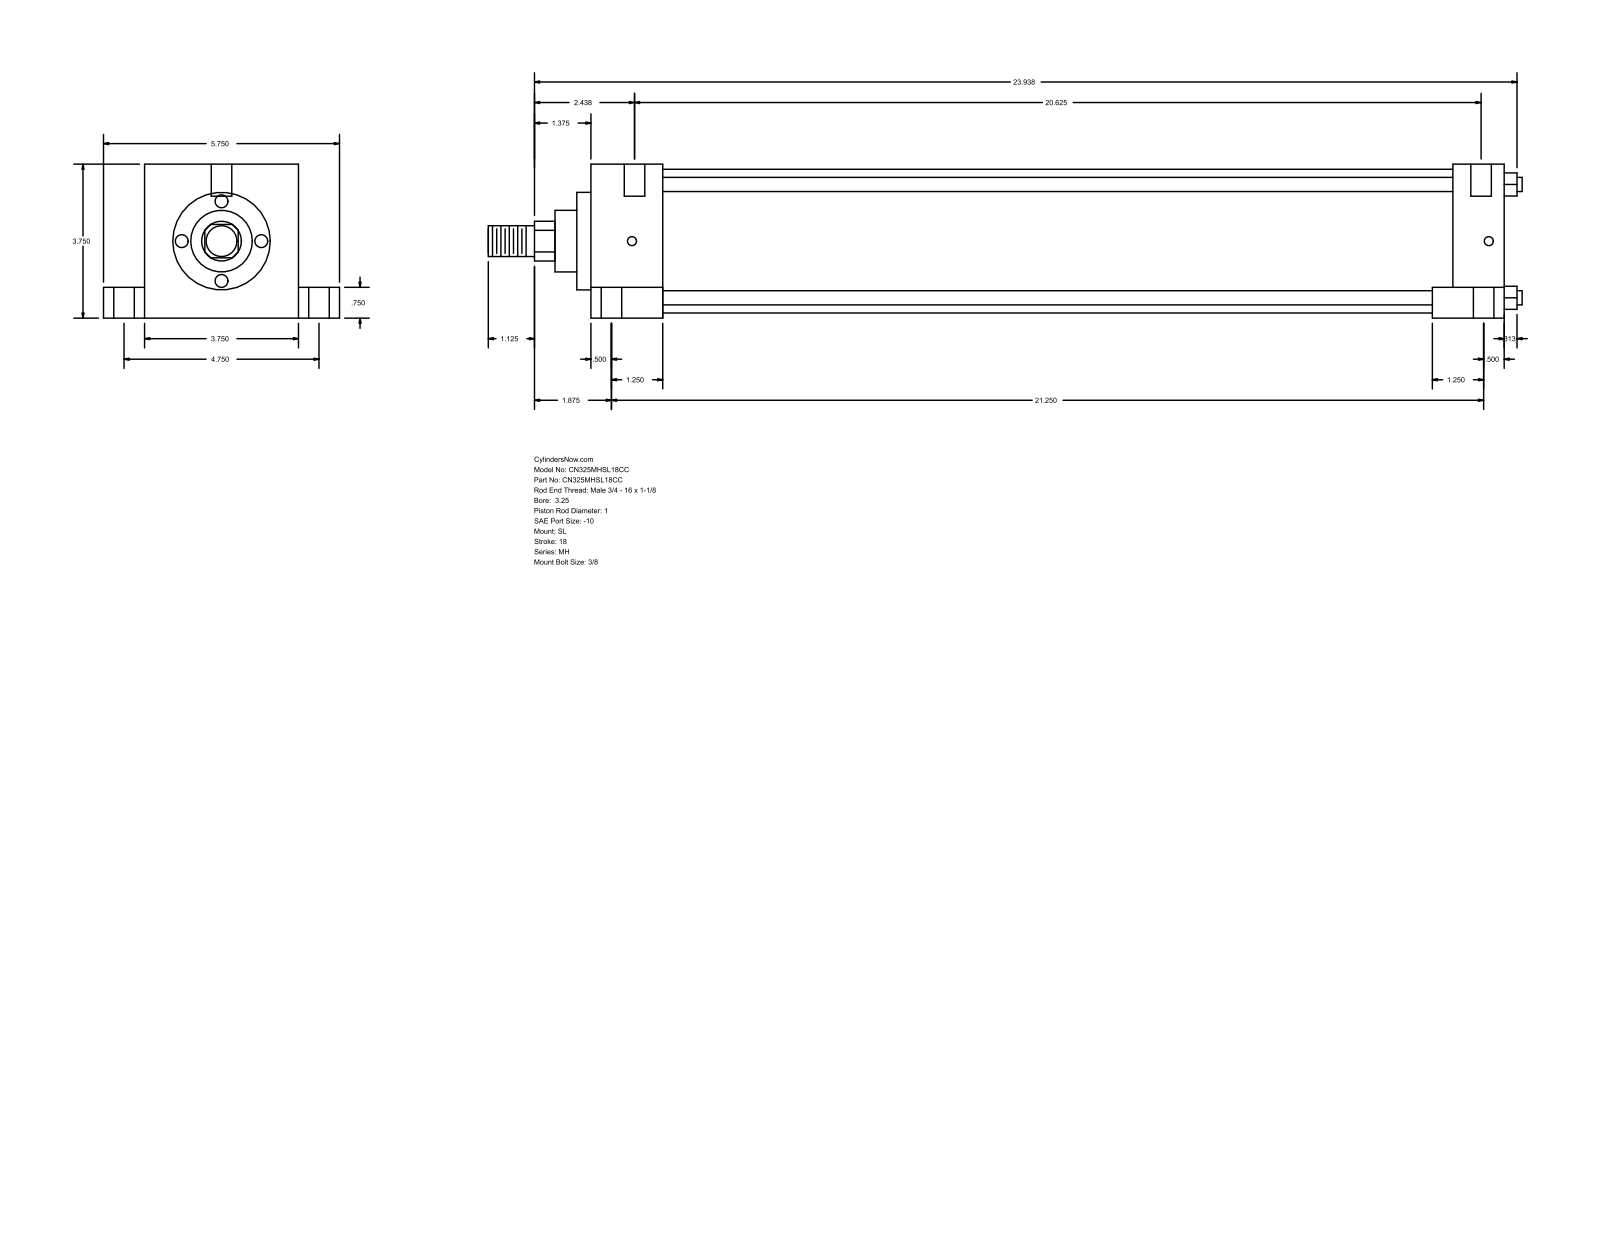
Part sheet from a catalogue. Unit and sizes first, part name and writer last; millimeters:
Units: millimetres
Overall size (bounding box): 639.76 × 146.05 × 95.25
Round holes (diameter × count): ⌀12.7 ×6, ⌀5.56 ×4, ⌀19.05 ×4
Round bosses / shafts (diameter × count): ⌀8.76 ×4, ⌀88.9 ×1, ⌀60.33 ×1, ⌀38.1 ×1, ⌀25.4 ×1, ⌀19.05 ×1
Partial cylindrical surfaces — rounded edges, fillets, slot ends (radius × count): R12.29 ×1
Main face-to-face distances: 95.24, 565.16, 44.46, 520.7, 25.41, 120.65, 19.05, 76.19, 533.41, 488.95
Hole centre spacings: 60.35, 60.41, 61.65, 62, 120.66, 528.92, 530.22, 530.49
Bodies: 0 solids, 110 faces (77 planar, 33 cylindrical, 0 other)
Part name (STEP PRODUCT): MH_SL__0325_1
STEP written by: GSSL Pune (CONFIG_CONTROL_DESIGN)
